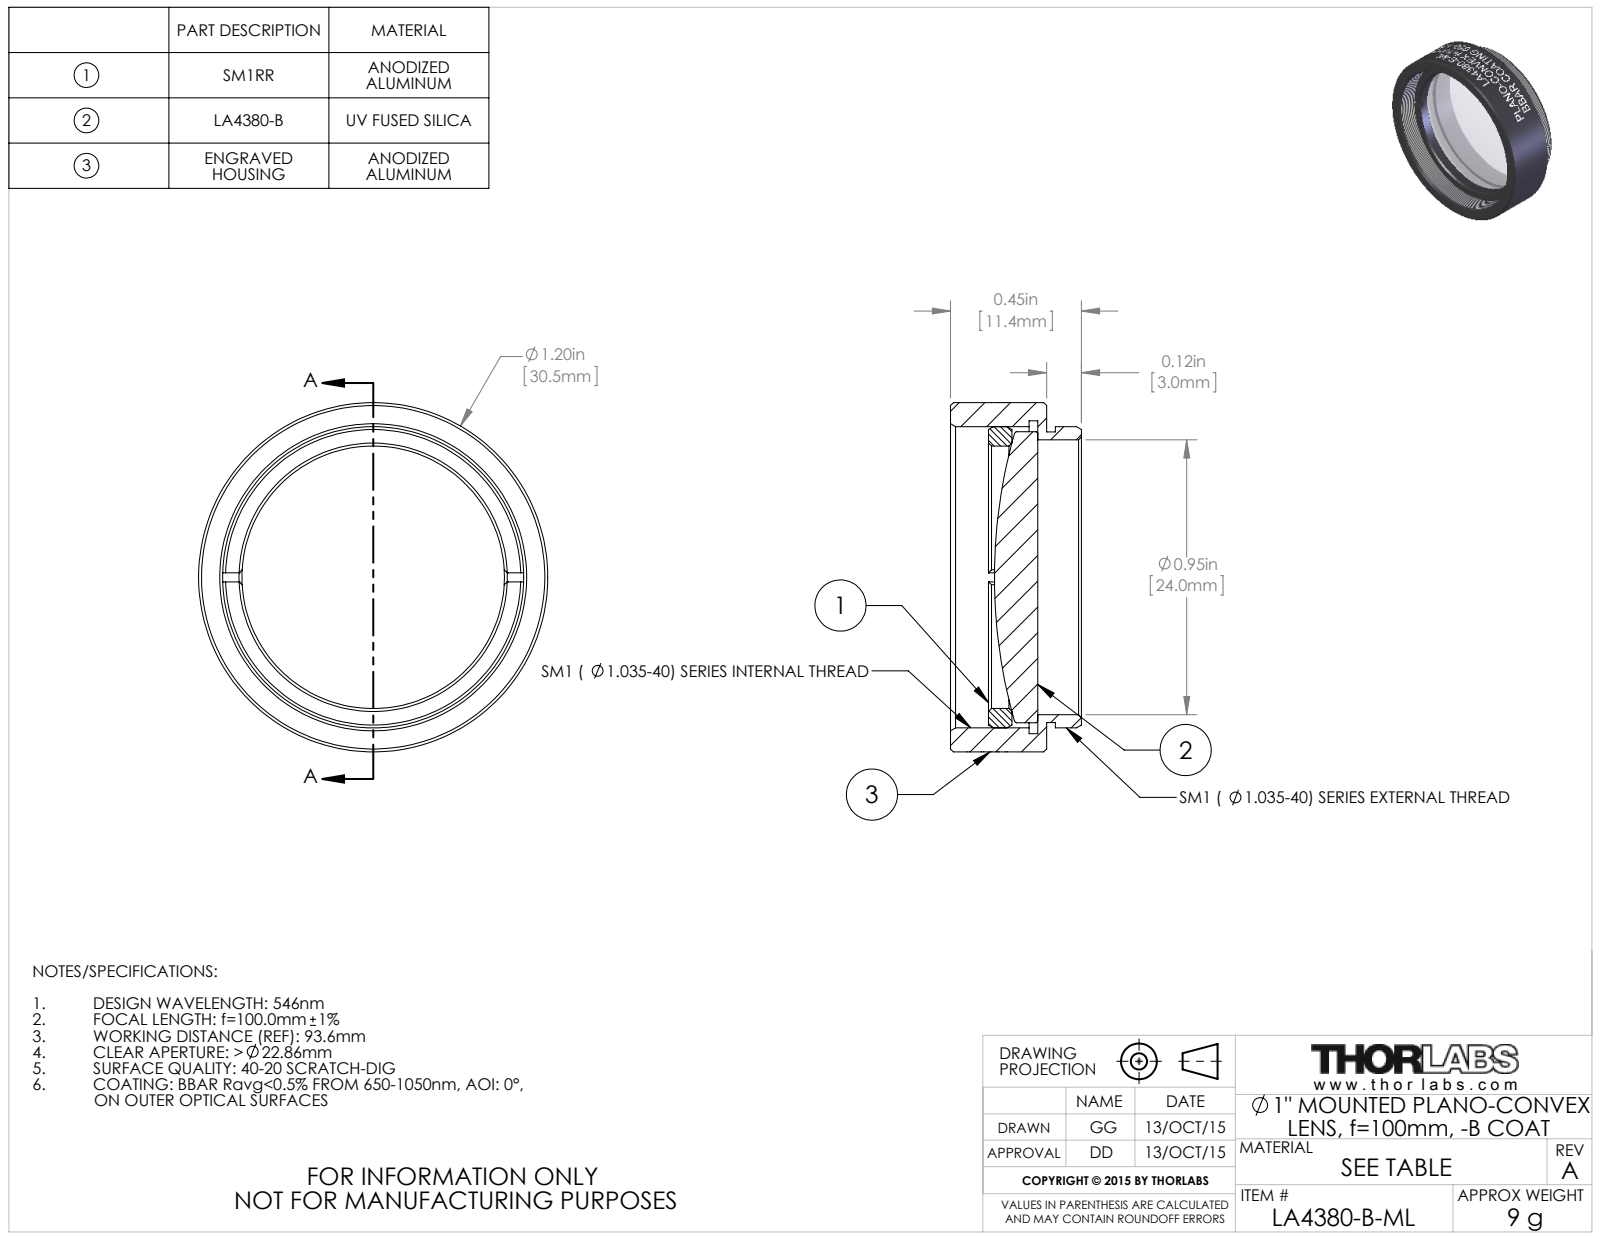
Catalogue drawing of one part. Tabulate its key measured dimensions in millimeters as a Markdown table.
| quantity | value |
| --- | --- |
| part name | TTN039266-E0W |
| STEP written by | SolidWorks 2014 (CONFIG_CONTROL_DESIGN) |
| units | millimeters |
| bodies | 3 solids, 165 faces (20 planar, 117 cylindrical, 28 other) |
| overall size | 30.48 × 30.48 × 11.43 |
| volume | 3 550 mm³ |
| surface area | 4 312 mm² |
| round holes (diameter × count) | 22.91 × 1, 24 × 1, 27.31 × 1 |
| round bosses / shafts (diameter × count) | 30.48 × 1, 26.29 × 1, 25.4 × 1, 25.37 × 1 |
| main face-to-face distances | 0.76, 8.38, 7.62, 3.04, 2.28, 5.34, 5.07, 4.31, 2.03, 3.31 |
